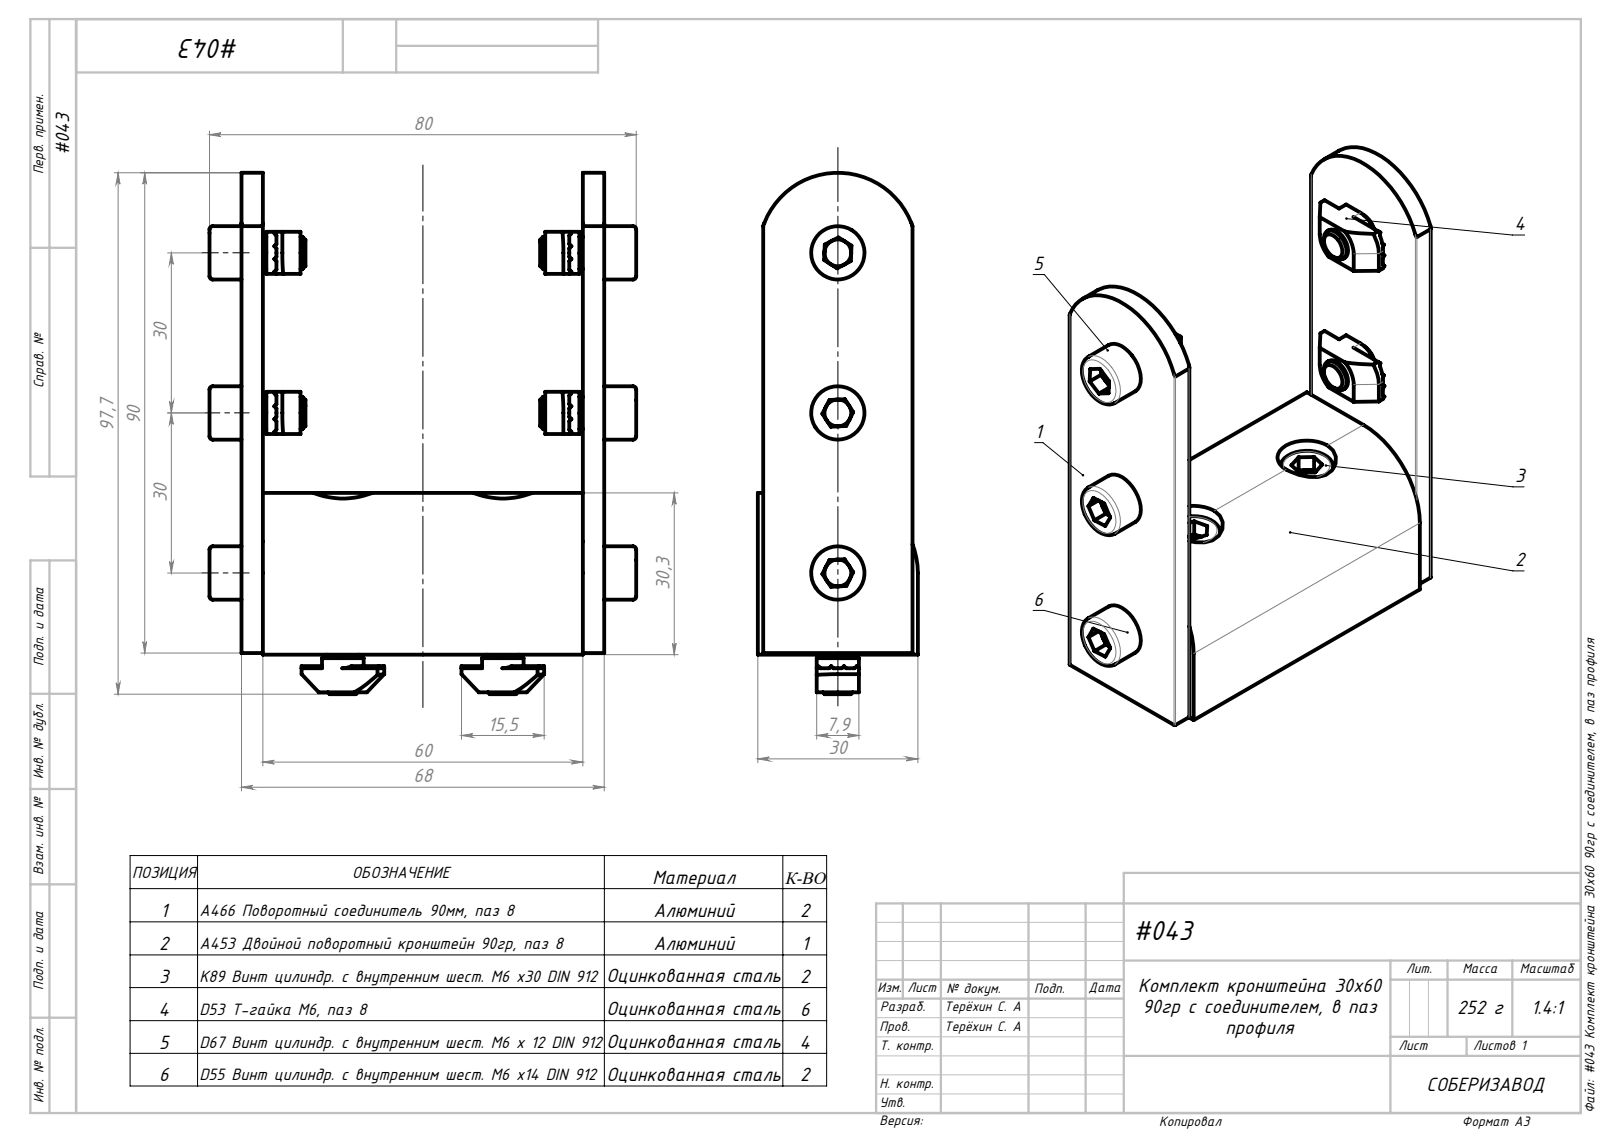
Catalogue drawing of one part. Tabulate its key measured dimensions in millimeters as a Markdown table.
| quantity | value |
| --- | --- |
| part name | D67 Винт цилиндр. с внутренним шест. М6 х 12 DIN 912; A453 Двойной поворотный кронштейн 90гр, паз 8; D55 Винт цилиндр. с внутренним шест. М6 х14 DIN 912; D53 Т-гайка М6, паз 8_00 (+3 more) |
| STEP written by | SolidWorks 2021 (AUTOMOTIVE_DESIGN) |
| units | millimeters |
| bodies | 17 solids, 551 faces (330 planar, 105 cylindrical, 116 other) |
| overall size | 97.7 × 80 × 30 |
| volume | 76 137 mm³ |
| surface area | 30 748 mm² |
| round holes (diameter × count) | 5 × 4, 6.4 × 3, 6.15 × 2, 11 × 2, 5.15 × 1 |
| round bosses / shafts (diameter × count) | 10 × 5, 6 × 5 |
| partial cylindrical surfaces (radius × count) | 4 × 12, 0.2 × 8, 6.87 × 8, 14.8 × 1, 15 × 1 |
| main face-to-face distances | 4, 64, 60, 68, 30, 1, 29, 30.3, 28, 11.05 |
| hole center spacings | 30, 60 |
